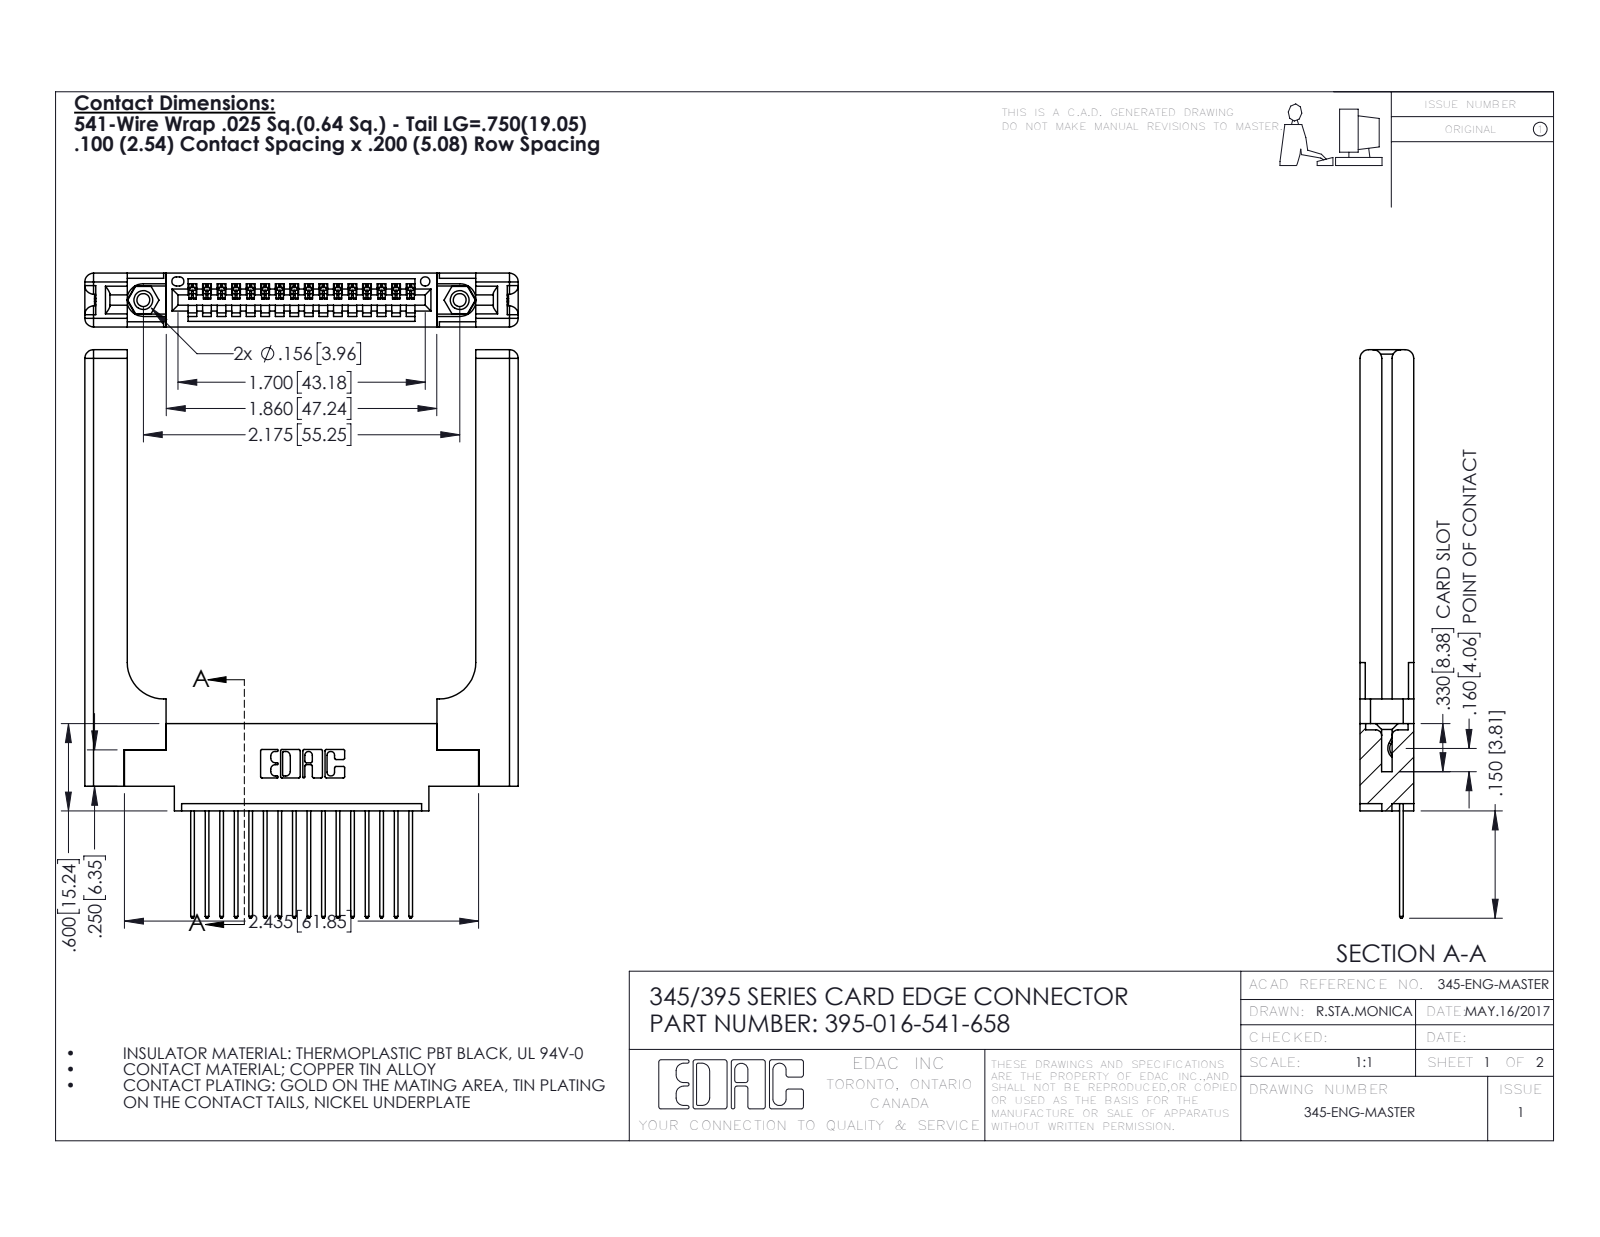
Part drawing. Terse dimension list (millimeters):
name: 345 Part_0.170 Offset - 0.156 Dia-TH; 345-220-058_345-220-058; 395-016-541-658; 345-250-001_345-250-001-102 (+1 more)
written by: SolidWorks 2016 (CONFIG_CONTROL_DESIGN)
unit: mm
bodies: 21 solids, 1314 faces (872 planar, 382 cylindrical, 60 other)
size: 99.2 × 75.7 × 9.4
volume: 15 400 mm³; area: 14 570 mm²
holes: 2× ⌀2.3, 2× ⌀3.2, 2× ⌀4, 1× ⌀1.6
bosses: 2× ⌀3.9
rounds: 32× R0.2, 32× R0.3, 22× R0.3, 16× R1.5, 6× R0.2, 6× R0.8, 3× R0.7, 2× R0.8
face distances: 9.4, 1.8, 7.6, 3.8, 3.8, 2, 5.6, 2.5, 6.9, 0.6
hole spacings: 6.9, 49.3, 55.2
